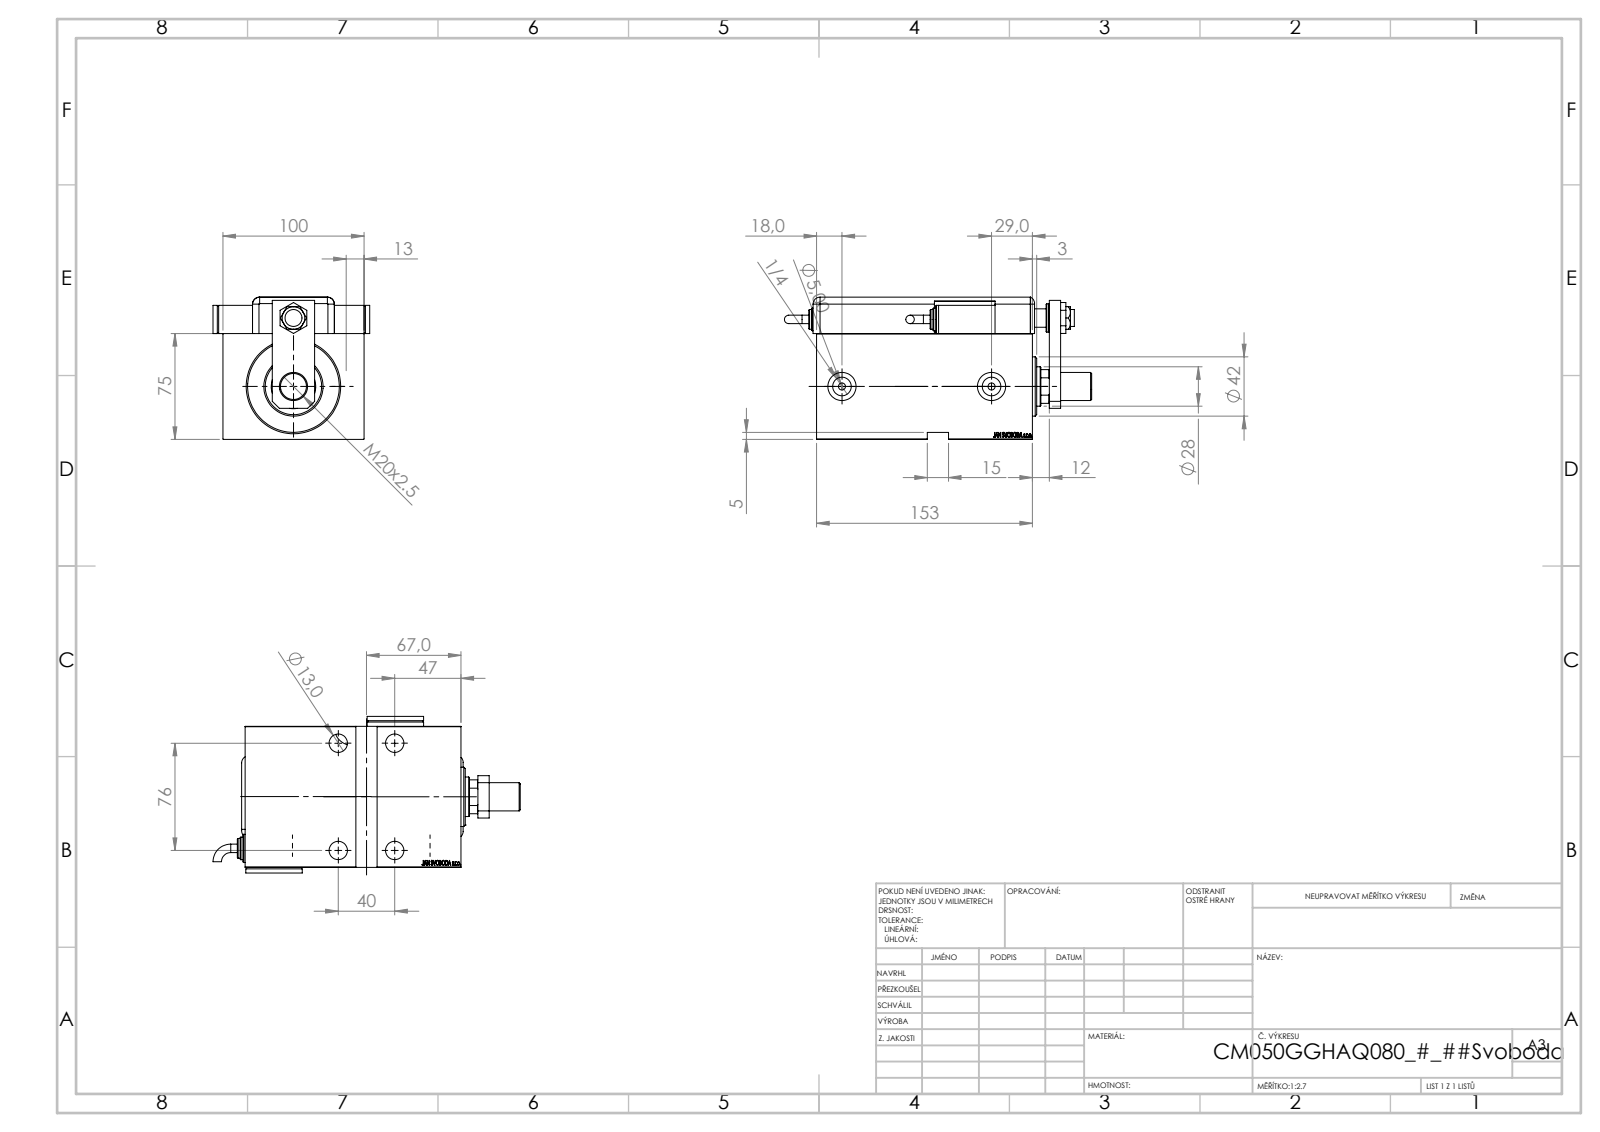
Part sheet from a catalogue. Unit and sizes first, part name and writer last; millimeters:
Units: millimetres
Overall size (bounding box): 217.76 × 111 × 100.8
Round holes (diameter × count): ⌀13 ×5, ⌀19 ×4, ⌀20 ×3, ⌀4 ×2, ⌀5 ×2, ⌀8 ×2, ⌀13.16 ×2, ⌀12 ×1, ⌀14 ×1, ⌀18.5 ×1, ⌀28 ×1, ⌀31.5 ×1
Round bosses / shafts (diameter × count): ⌀20 ×3, ⌀18 ×3, ⌀16 ×2, ⌀14 ×2, ⌀6 ×2, ⌀42 ×1
Partial cylindrical surfaces — rounded edges, fillets, slot ends (radius × count): R5 ×9, R10 ×1, R13.5 ×1
Main face-to-face distances: 3, 75, 100, 100.8, 25.8, 153, 5, 22.8, 97.8, 14
Hole centre spacings: 40, 47.2, 61.22, 76, 82.87, 85.88, 91.59, 20
Volume: 1 145 000 mm³ · Surface area: 207 360 mm²
Bodies: 16 solids, 1292 faces (650 planar, 115 cylindrical, 527 other)
Part name (STEP PRODUCT): SWITCH DIM A_G; KRYT; V450CM_G_VCP; SWITCH Q (+7 more)
STEP written by: SolidWorks 2019 (CONFIG_CONTROL_DESIGN)
